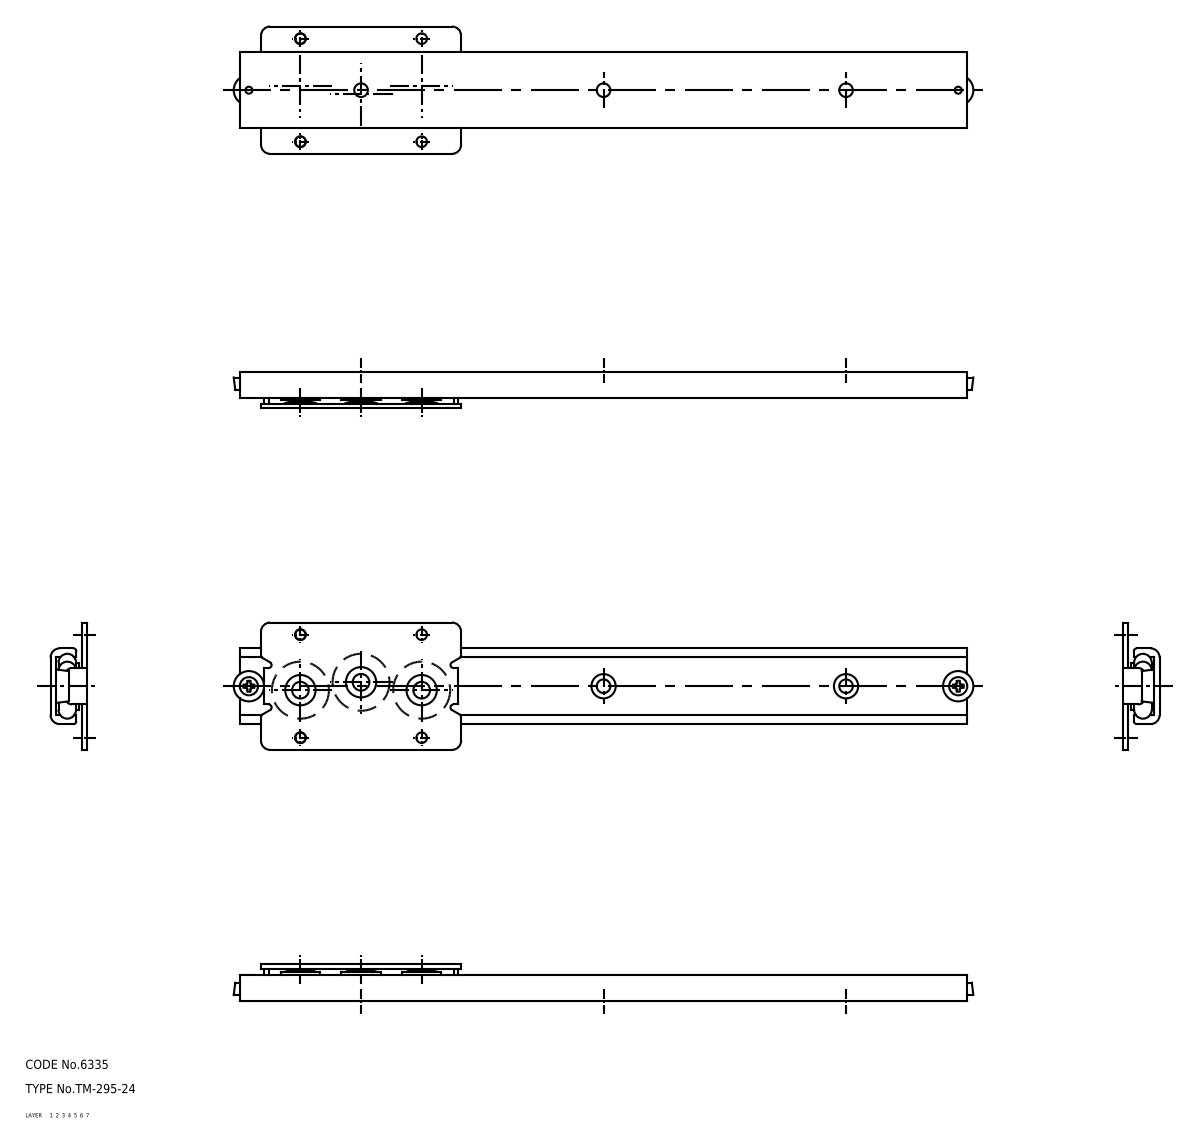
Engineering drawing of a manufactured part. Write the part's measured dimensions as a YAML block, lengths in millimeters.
part_name: "67120634; 67120647; 67120660; 67120673 (+3 more)"
step_written_by: "CADfix (AUTOMOTIVE_DESIGN)"
units: millimeters
bodies: {solids: 7, faces: 208, planar: 0, cylindrical: 0, other: 208}
overall_size: [244, 42, 12]
volume: 27050
surface_area: 28046
